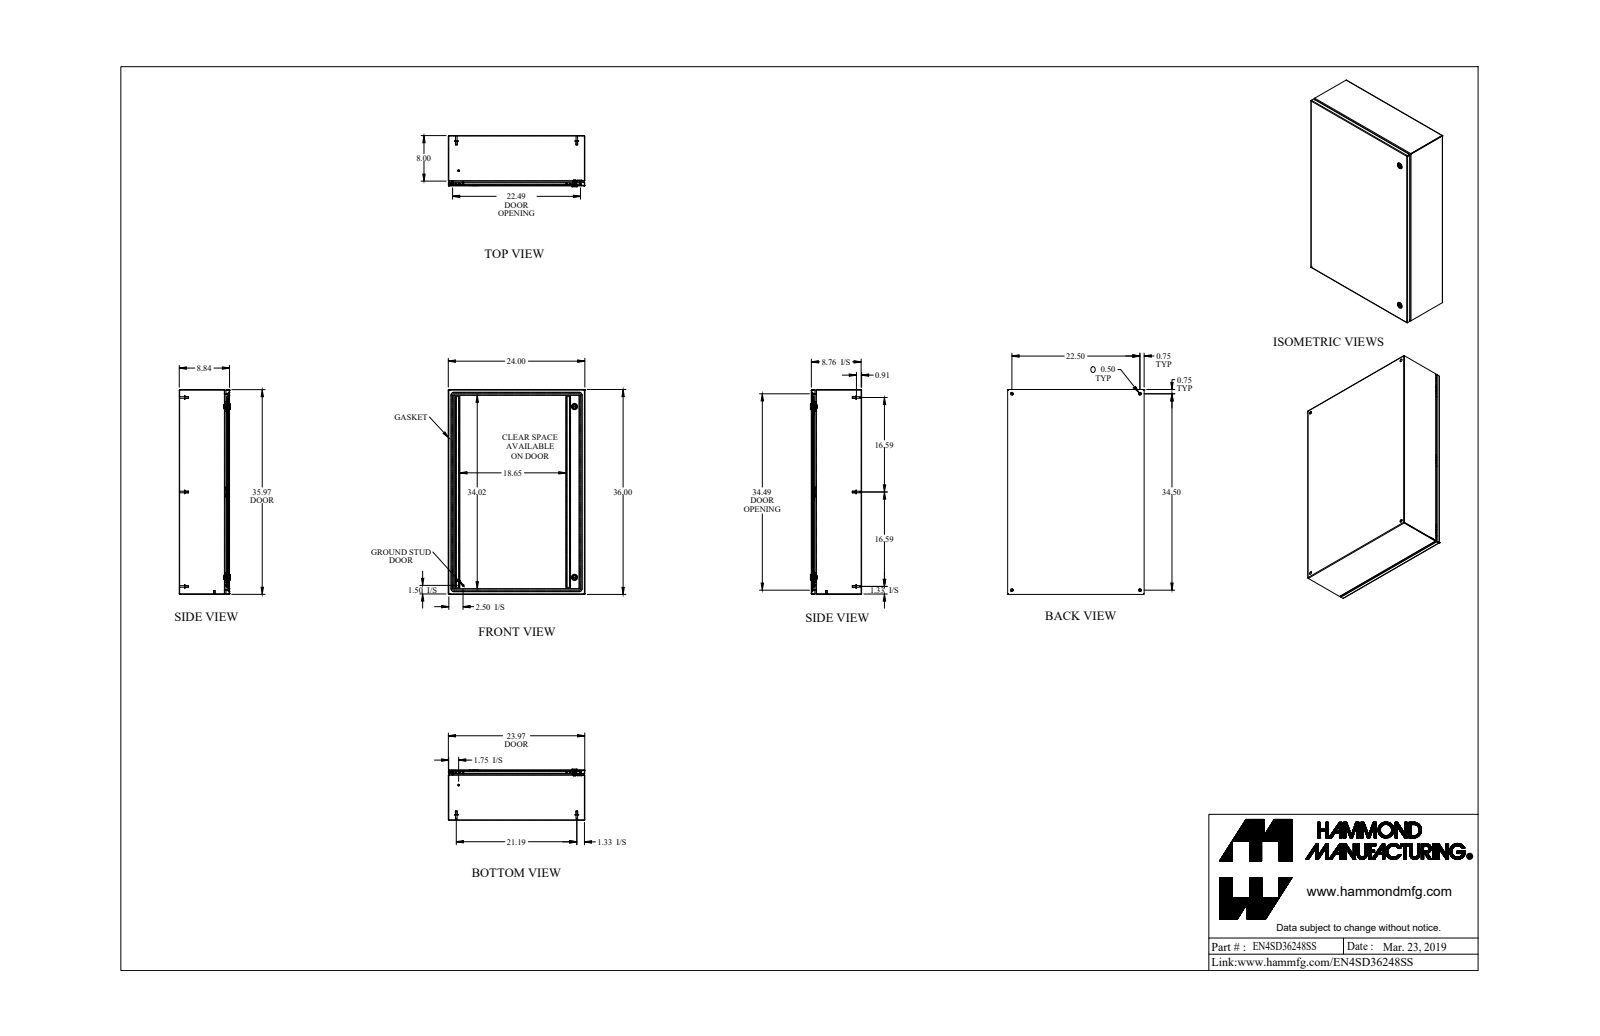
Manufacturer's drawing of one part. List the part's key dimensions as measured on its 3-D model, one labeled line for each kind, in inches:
Part name (STEP PRODUCT): EN4SD36248SS_Default
STEP written by: SolidWorks 2019 (CONFIG_CONTROL_DESIGN)
Units: inches
Bodies: 35 solids, 959 faces (458 planar, 313 cylindrical, 188 other)
Overall size (bounding box): 36 × 24 × 9.002
Volume: 226.9 in³ · Surface area: 6 380 in²
Round holes (diameter × count): ⌀0.5 ×6, ⌀0.197 ×2, ⌀0.387 ×2, ⌀0.63 ×2, ⌀0.768 ×2, ⌀0.172 ×1, ⌀0.24 ×1, ⌀0.242 ×1
Round bosses / shafts (diameter × count): ⌀0.625 ×8, ⌀0.313 ×8, ⌀0.275 ×6, ⌀1.1 ×2, ⌀0.785 ×2, ⌀0.525 ×2, ⌀0.25 ×2, ⌀0.236 ×2
Partial cylindrical surfaces — rounded edges, fillets, slot ends (radius × count): R0.036 ×20, R0.108 ×20, R0.25 ×16, R0.01 ×12, R0.048 ×12, R0.006 ×6, R0.062 ×6, R0.125 ×4
Main face-to-face distances: 0.072, 8.77, 8.698, 8.842, 23.928, 35.928, 23.856, 24, 35.856, 36
Hole centre spacings: 2.488, 21.557, 22.5, 32.267, 34.5, 38.726, 41.189, 30
